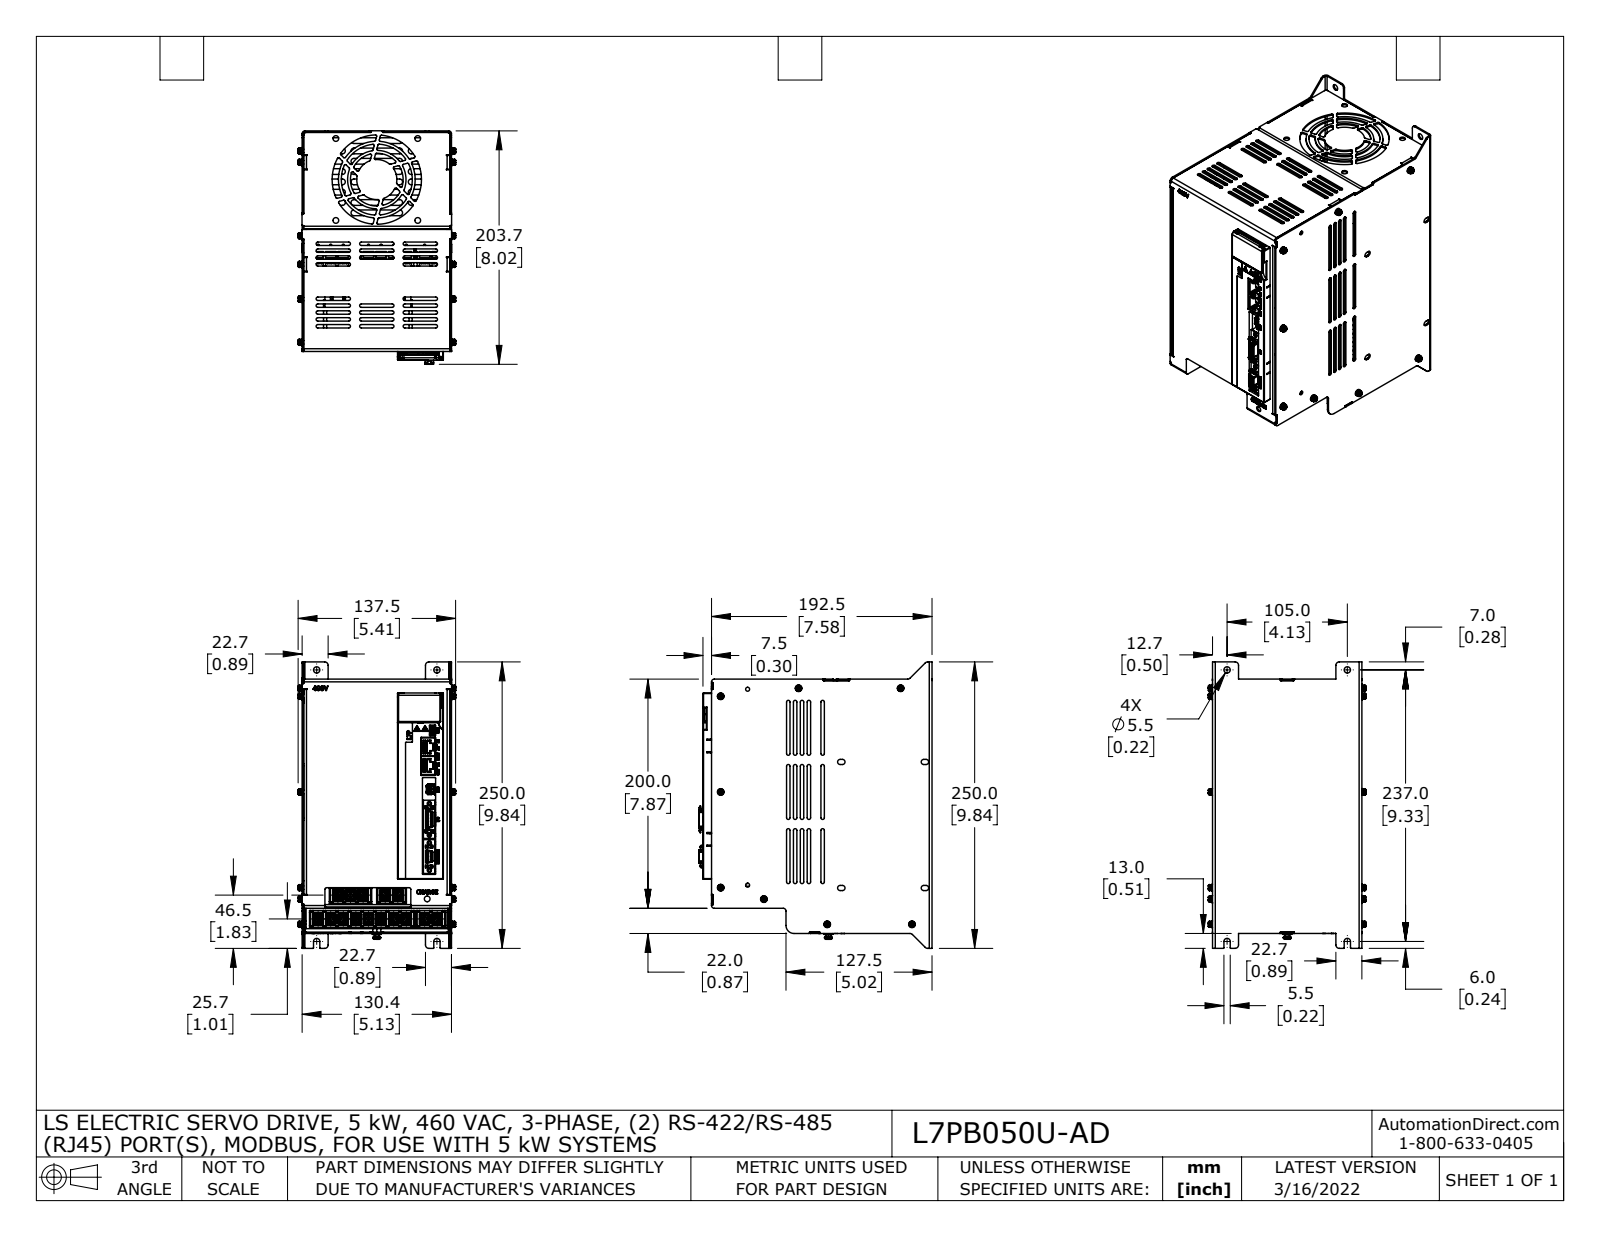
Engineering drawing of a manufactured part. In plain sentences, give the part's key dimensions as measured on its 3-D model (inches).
The part is named "L7PB (5kW) redsurfs1 r1 200 faces red1r1 redsurfs1b r1Bc cmb extw fxt coord 21bb NEWaCb fxt". Its 3-D file was written by "SolidWorks 2021 (AUTOMOTIVE_DESIGN)". It is 28 solids with 5237 faces: 3541 planar, 1225 cylindrical and 471 other. Overall it measures 9.843 by 8.024 by 5.413 inches. Its volume is 316.2 cubic inches and its surface area 403.5 square inches. Round holes: 8 of diameter 0.14, 4 of diameter 0.15, 2 of diameter 0.079, 2 of diameter 0.102, 2 of diameter 0.217, 1 of diameter 0.071, 1 of diameter 0.098, 1 of diameter 0.197, 1 of diameter 3.071. Round bosses or shafts: 15 of diameter 0.315, 8 of diameter 0.228, 8 of diameter 0.209, 8 of diameter 0.196, 8 of diameter 0.118, 2 of diameter 0.031, 1 of diameter 1.378, 1 of diameter 0.307. Partial cylindrical surfaces (rounded edges, fillets, slot ends): 237 of radius 0.02, 157 of radius 0.039, 64 of radius 0.035, 24 of radius 0.008, 21 of radius 0.059, 13 of radius 0.031, 12 of radius 0.094, 11 of radius 0.012. The main face-to-face distances are 5.134, 7.579, 5.133, 8.739, 0.047, 0.024, 7.874, 8.738, 1.574, 7.164. The hole center spacings are 3.287, 0.274, 0.446, 0.931, 0.992, 1.081, 1.204, 1.354.
